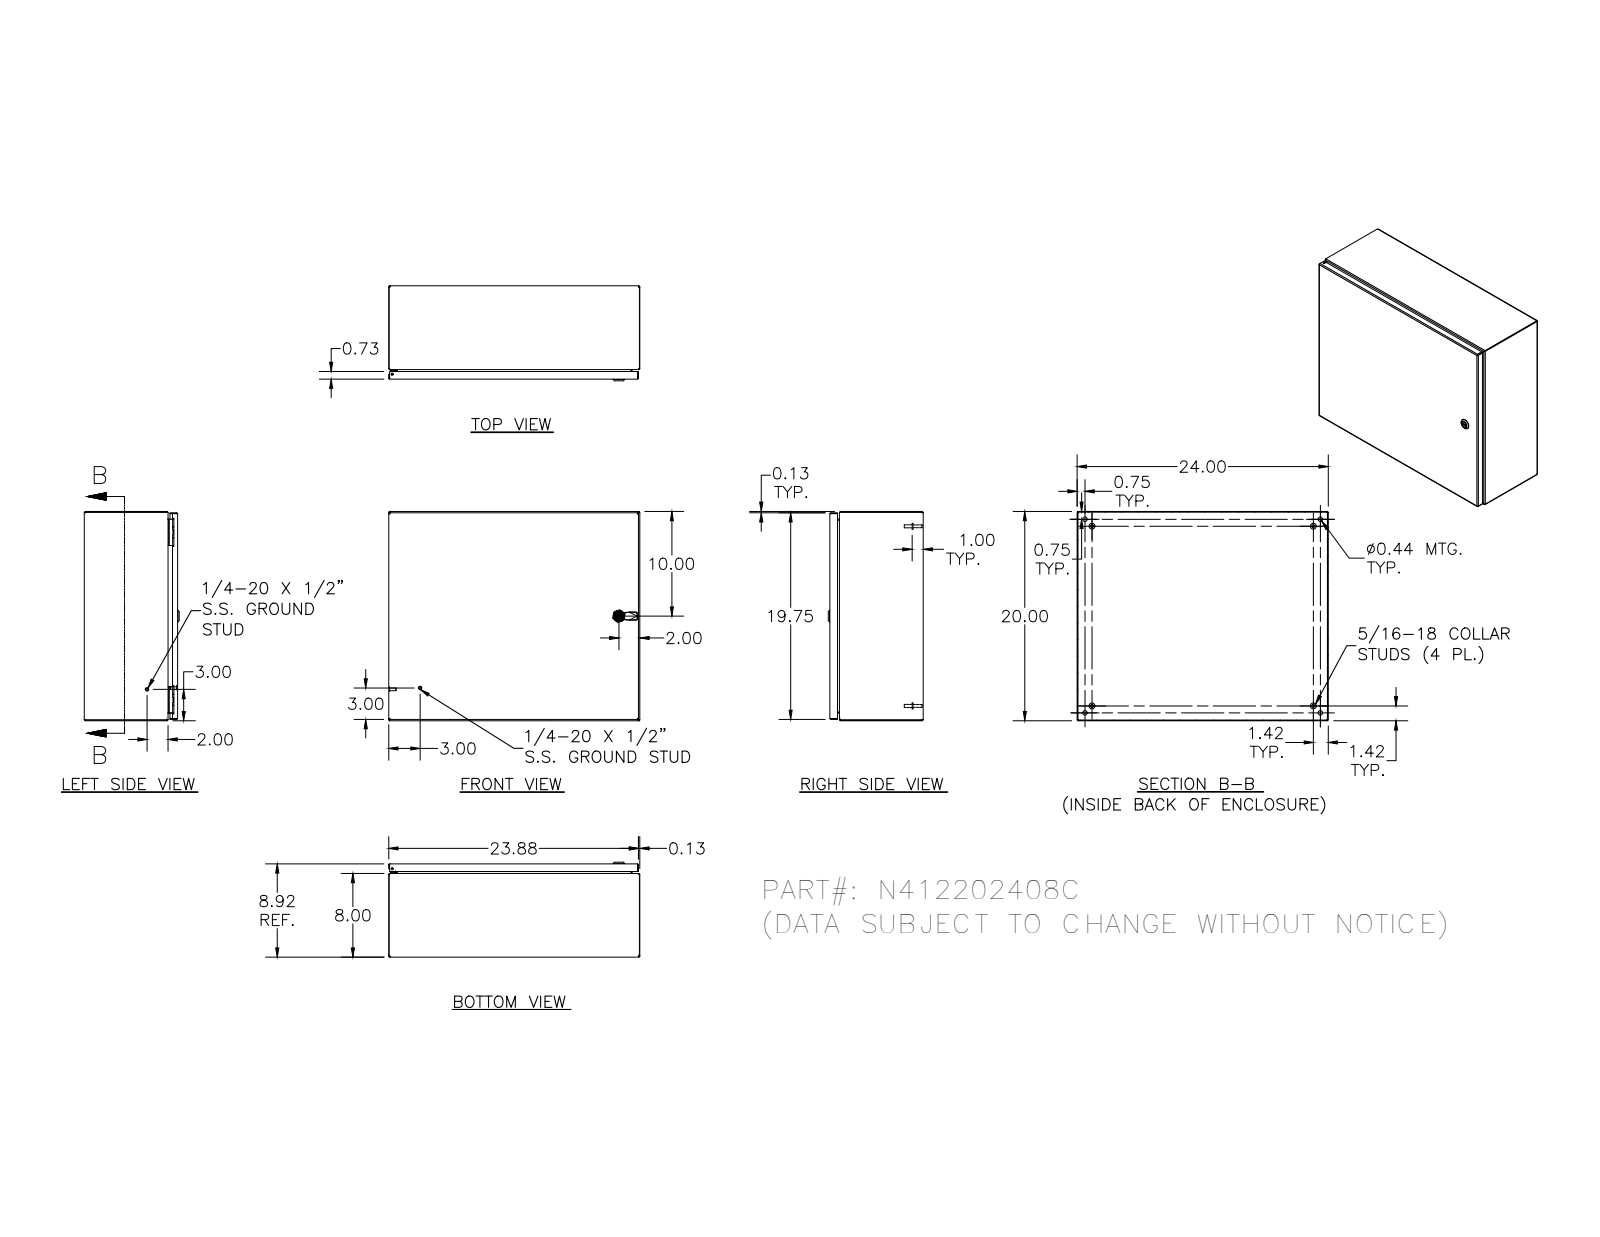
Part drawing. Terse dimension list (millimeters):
name: N412202408C
written by: SolidWorks 2018 (AUTOMOTIVE_DESIGN)
unit: mm
bodies: 33 solids, 1449 faces (530 planar, 547 cylindrical, 372 other)
size: 609.6 × 508 × 230.5
volume: 2 232 000 mm³; area: 2 389 000 mm²
holes: 5× ⌀4.8, 4× ⌀2.4, 4× ⌀3.9, 4× ⌀4.2, 4× ⌀4.4, 4× ⌀11.1, 2× ⌀4, 1× ⌀4.7, 1× ⌀5, 1× ⌀8, 1× ⌀10, 1× ⌀10.2
bosses: 10× ⌀6.4, 4× ⌀14.3, 4× ⌀9.1, 4× ⌀8.1, 4× ⌀7.6, 4× ⌀7, 4× ⌀6.5, 4× ⌀4.2
rounds: 30× R0.3, 30× R0.8, 26× R1.3, 20× R2.7, 18× R0.4, 16× R3.2, 13× R0.5, 8× R0.8
face distances: 1.9, 224.6, 222.7, 226.5, 1.9, 506.1, 508, 504.2, 506.1, 607.7
hole spacings: 406.4, 16.8, 16.7, 33.2, 49.9, 389.6, 423.2, 12.7
